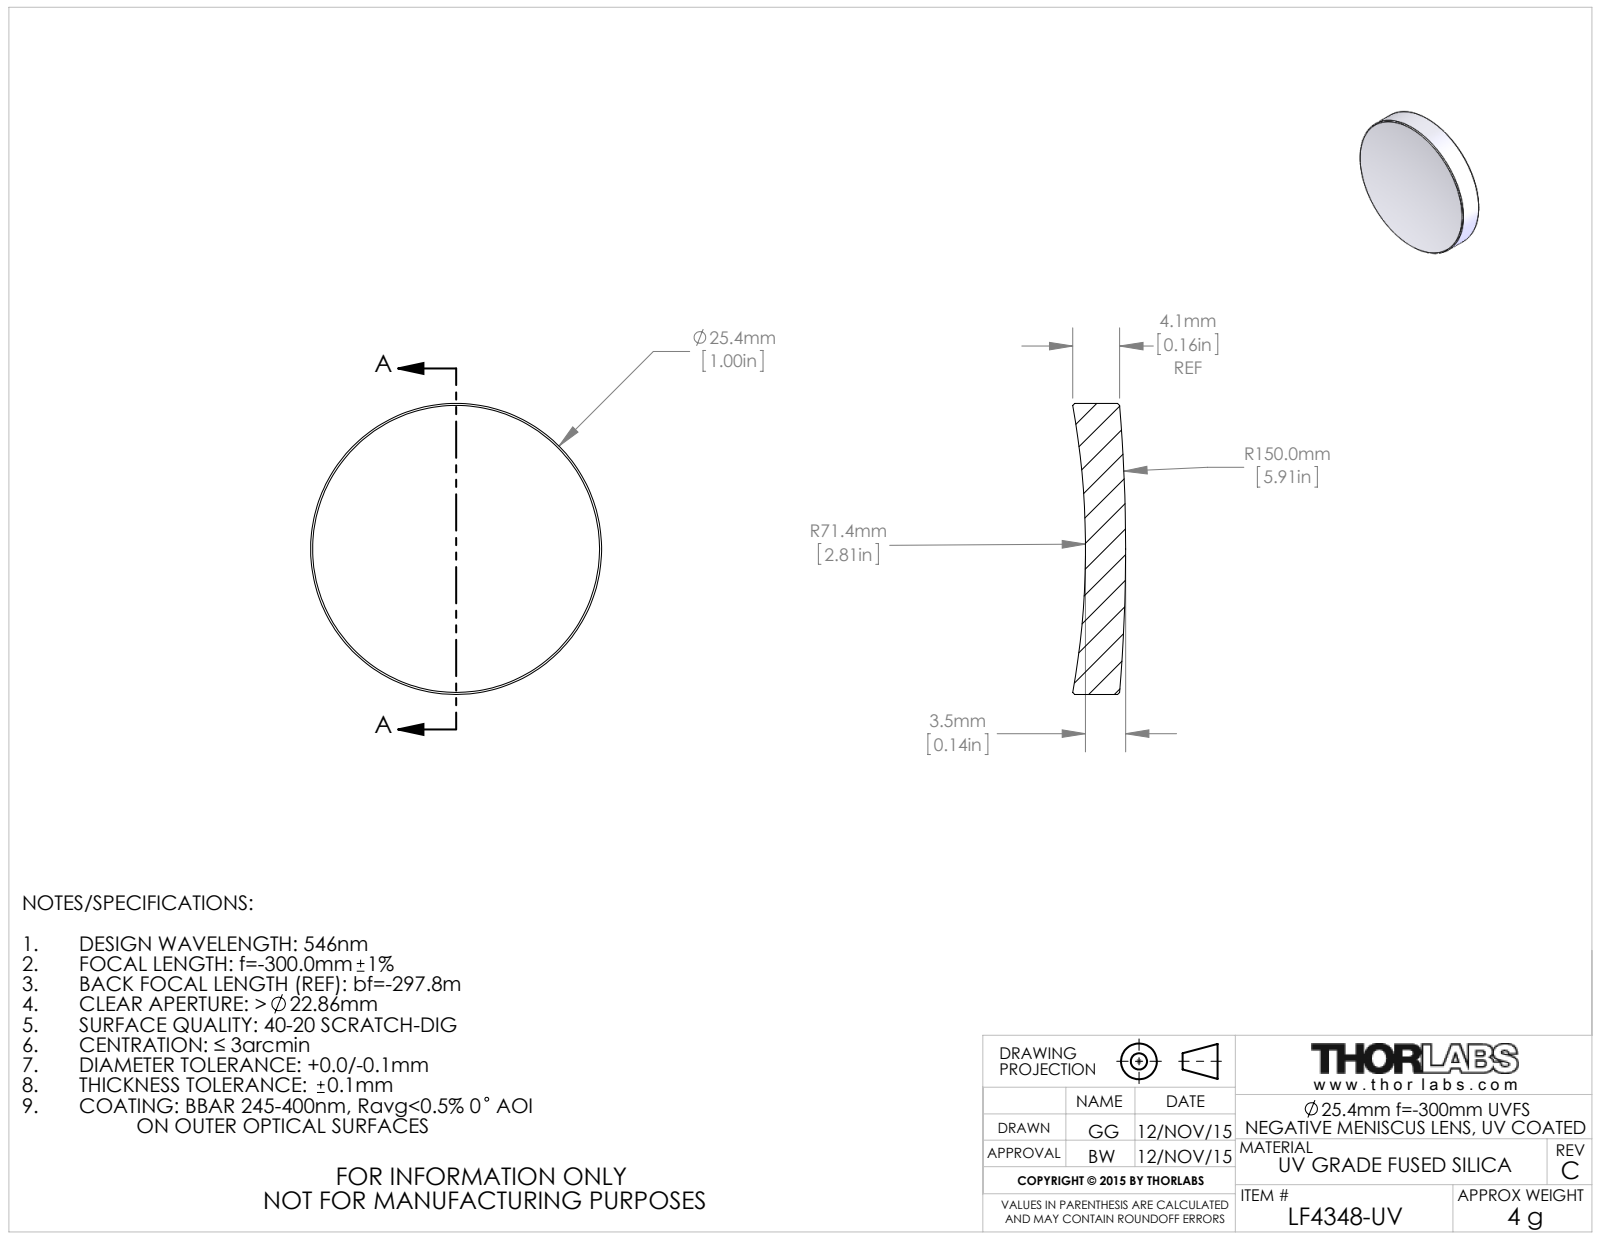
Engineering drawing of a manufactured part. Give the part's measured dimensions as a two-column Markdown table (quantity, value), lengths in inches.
| quantity | value |
| --- | --- |
| part name | 4940-E0W |
| STEP written by | SolidWorks 2014 (CONFIG_CONTROL_DESIGN) |
| units | inches |
| bodies | 1 solid, 10 faces (0 planar, 2 cylindrical, 8 other) |
| overall size | 1 × 1 × 0.181 |
| volume | 0.117 in³ |
| surface area | 2.058 in² |
| round bosses / shafts (diameter × count) | 1 × 1 |
